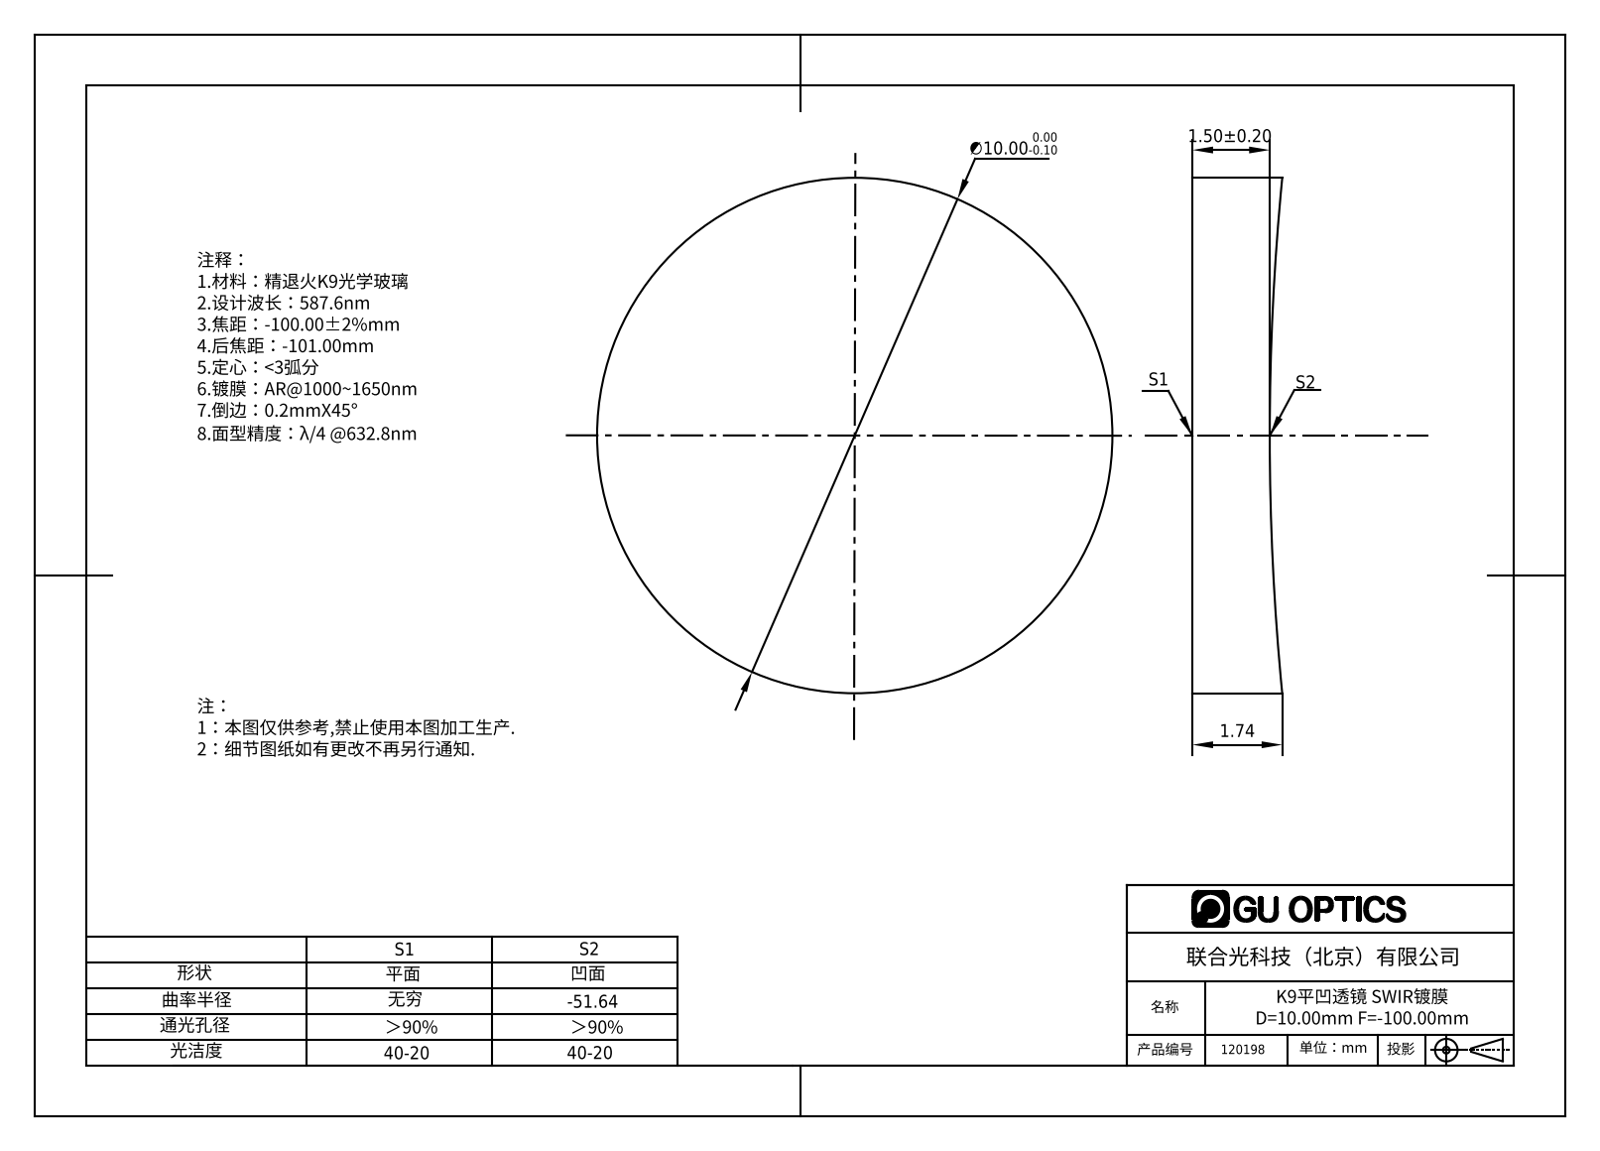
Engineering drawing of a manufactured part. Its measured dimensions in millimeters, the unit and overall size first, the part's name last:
Units: millimetres
Overall size (bounding box): 10 × 10 × 1.74
Round bosses / shafts (diameter × count): ⌀10 ×1
Volume: 127 mm³ · Surface area: 212 mm²
Bodies: 1 solid, 5 faces (1 planar, 2 cylindrical, 2 other)
Part name (STEP PRODUCT): 120138
STEP written by: SolidWorks 2016 (AUTOMOTIVE_DESIGN)
